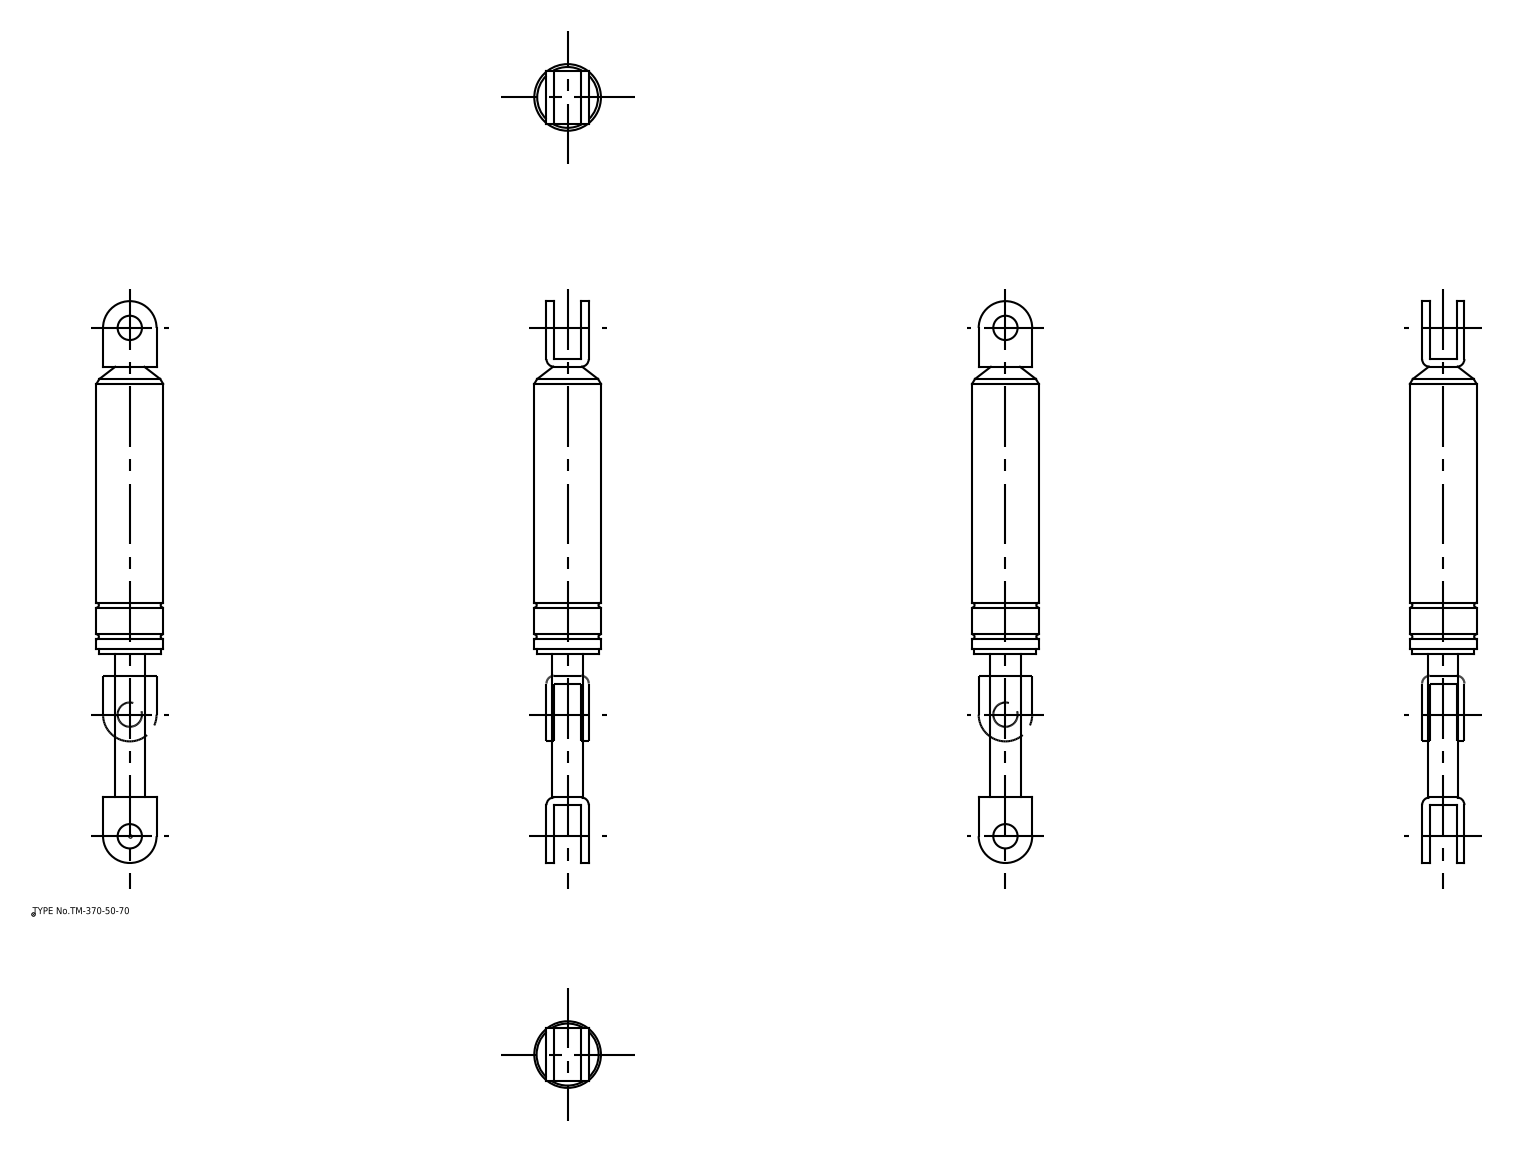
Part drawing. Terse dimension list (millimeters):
name: TM_370_50_70; TM_370_50_70_div
written by: spGate 16.7.1 (AUTOMOTIVE_DESIGN)
unit: mm
bodies: 2 solids, 64 faces (22 planar, 32 cylindrical, 10 other)
size: 231 × 28.2 × 28.2
volume: 82 498 mm³; area: 19 256 mm²
holes: 2× ⌀10
bosses: 1× ⌀28.2, 1× ⌀27.4, 1× ⌀25.5, 1× ⌀12.5
rounds: 4× R3.2, 2× R11
face distances: 3.2, 14.2, 17.4, 11, 22, 180.2, 62.2, 183.4, 121.2, 118
hole spacings: 209
